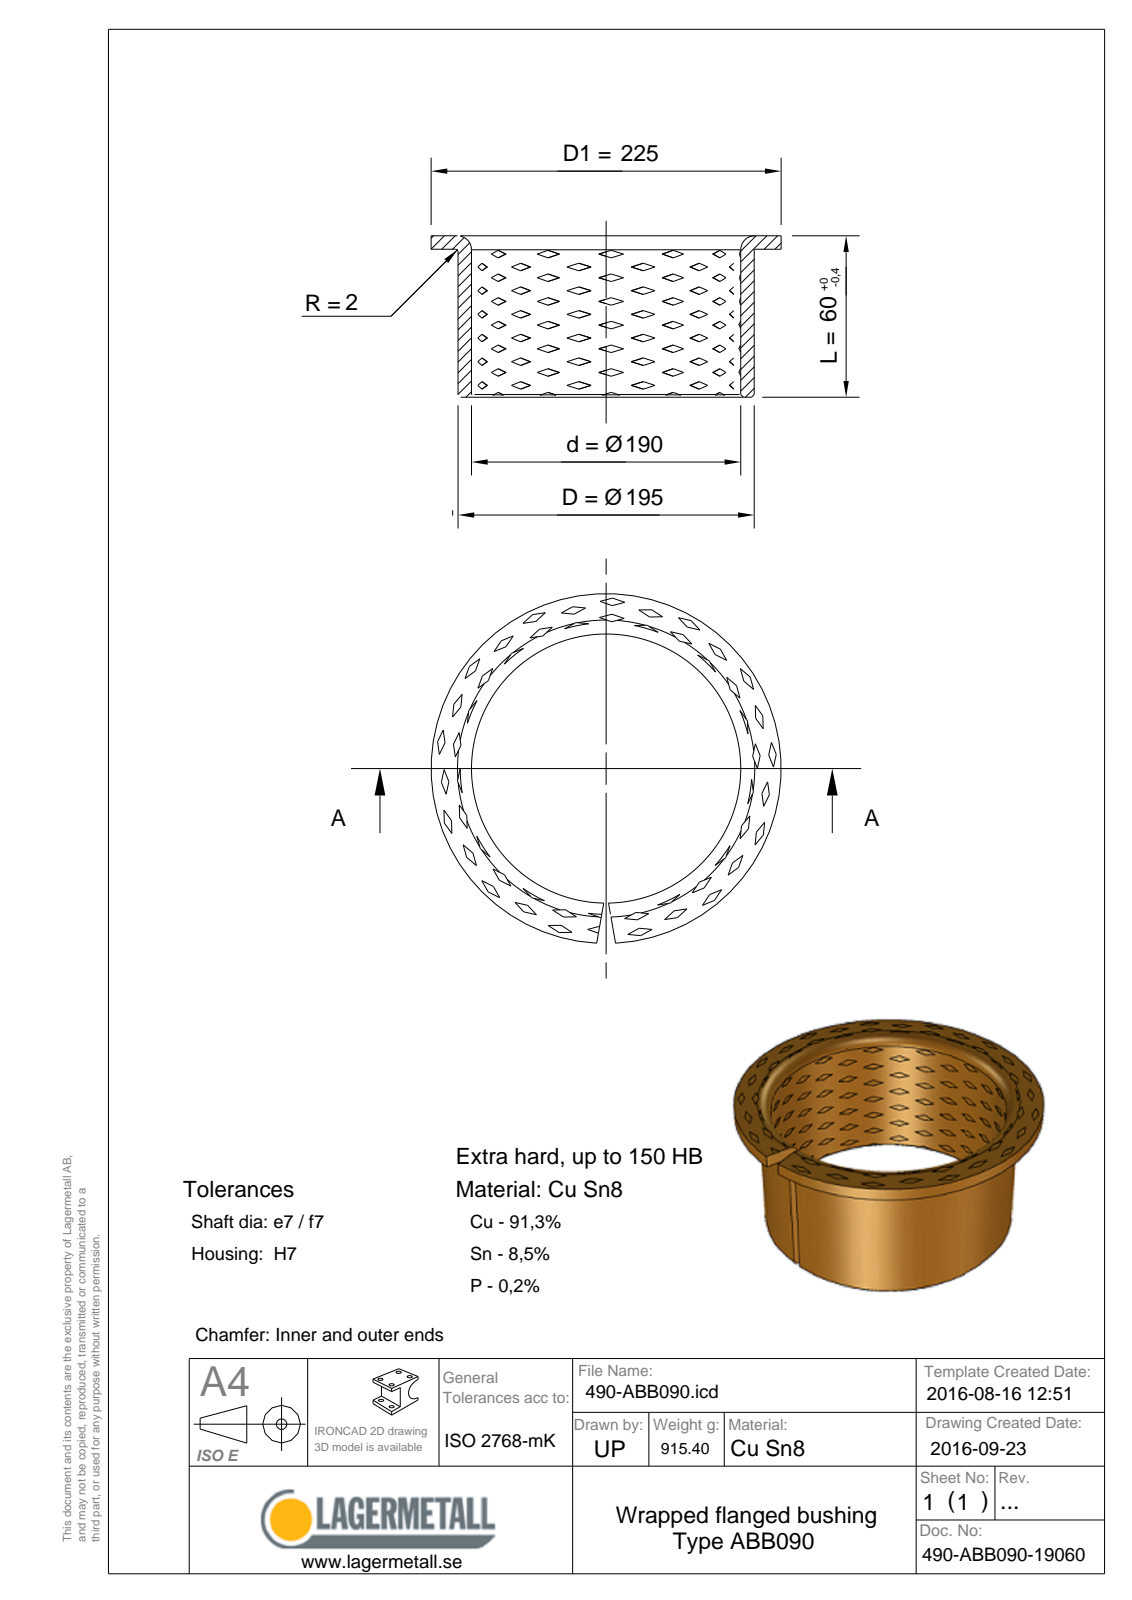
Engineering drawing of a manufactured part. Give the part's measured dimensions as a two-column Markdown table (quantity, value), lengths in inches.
| quantity | value |
| --- | --- |
| STEP written by | Spatial InterOp 3D (CONFIG_CONTROL_DESIGN) |
| units | inches |
| bodies | 1 solid, 26 faces (5 planar, 9 cylindrical, 12 other) |
| overall size | 8.858 × 8.858 × 2.362 |
| volume | 6.896 in³ |
| surface area | 145.4 in² |
| round holes (diameter × count) | 7.48 × 1 |
| round bosses / shafts (diameter × count) | 8.858 × 1, 7.677 × 1 |
| main face-to-face distances | 0.098, 2.264, 2.362 |
